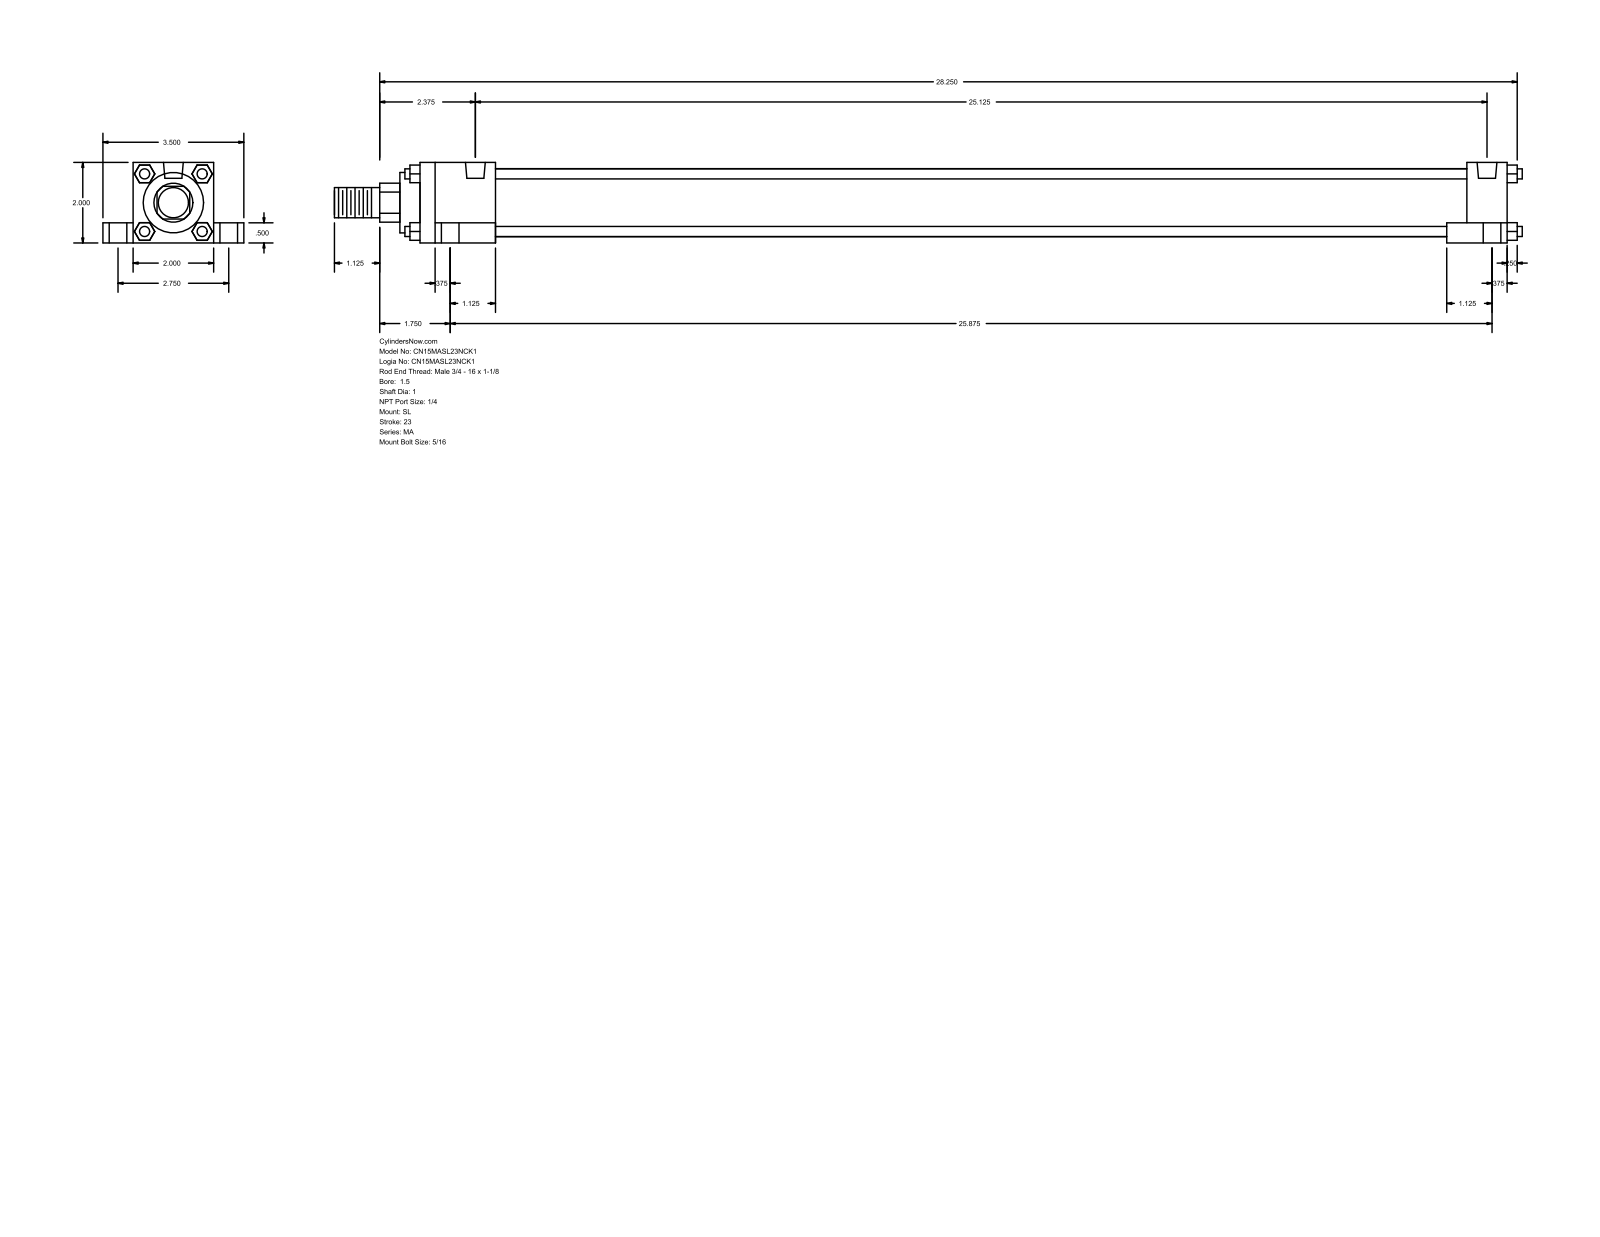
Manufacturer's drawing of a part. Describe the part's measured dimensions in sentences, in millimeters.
The part is named "MA_SL__0150_1". Its 3-D file was written by "GSSL Pune (CONFIG_CONTROL_DESIGN)". It is 0 solids with 148 faces: 112 planar, 36 cylindrical and 0 other. Overall it measures 749.3 by 88.9 by 50.8 millimeters. Round holes: 4 of diameter 7.94, 4 of diameter 11.11, 4 of diameter 17.46, 2 of diameter 12.49. Round bosses or shafts: 4 of diameter 6.35, 1 of diameter 42.93, 1 of diameter 38.1, 1 of diameter 25.4, 1 of diameter 19.05. Partial cylindrical surfaces (rounded edges, fillets, slot ends): 1 of radius 12.29. The main face-to-face distances are 50.8, 12.7, 19.05, 69.85, 38.1, 9.52, 685.8, 25.4, 6.35, 660.4. The hole center spacings are 35.06, 38.36, 69.84, 638.17, 642.29, 654.98, 657.22, 660.92.
